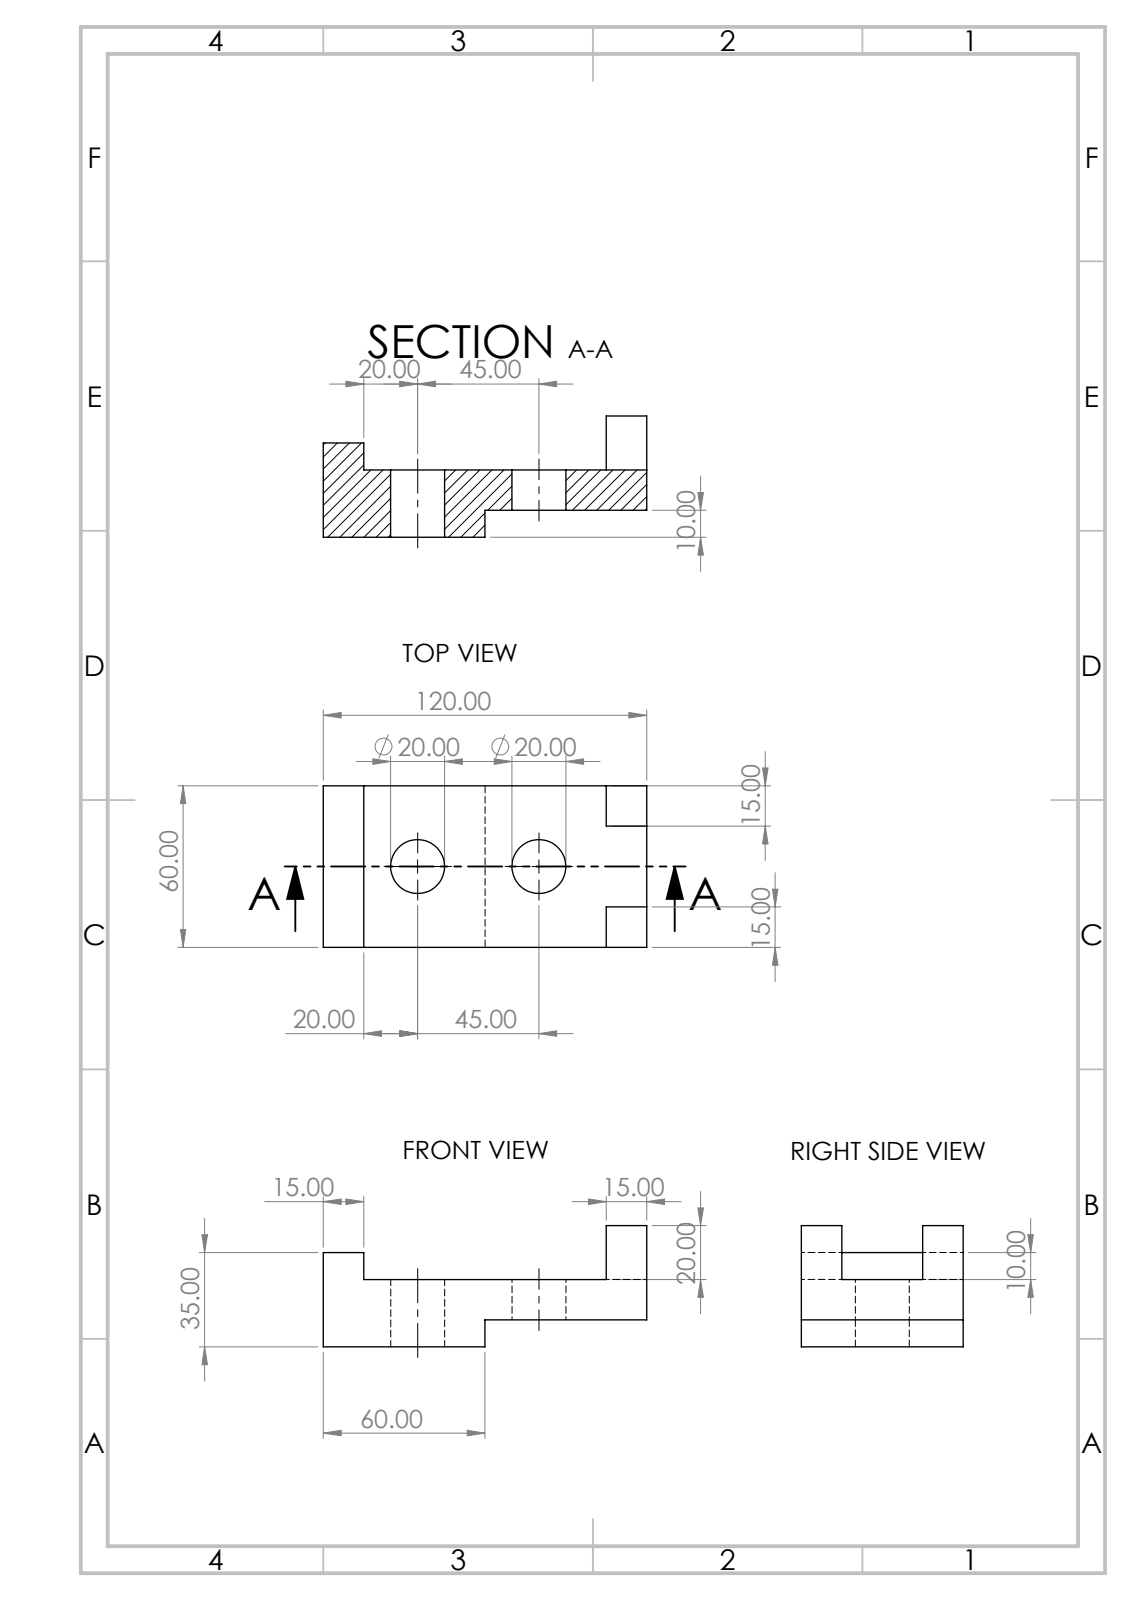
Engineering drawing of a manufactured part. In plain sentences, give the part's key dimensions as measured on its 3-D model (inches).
Its 3-D file was written by "Autodesk Inventor 2021 (AUTOMOTIVE_DESIGN)". It is 1 solid with 71 faces: 3 planar, 0 cylindrical and 68 other. Overall it measures 6.102 by 2.953 by 2.953 inches. Its volume is 2.499 cubic inches and its surface area 142.2 square inches. The main face-to-face distances are 0.039, 6.102, 6.063.
